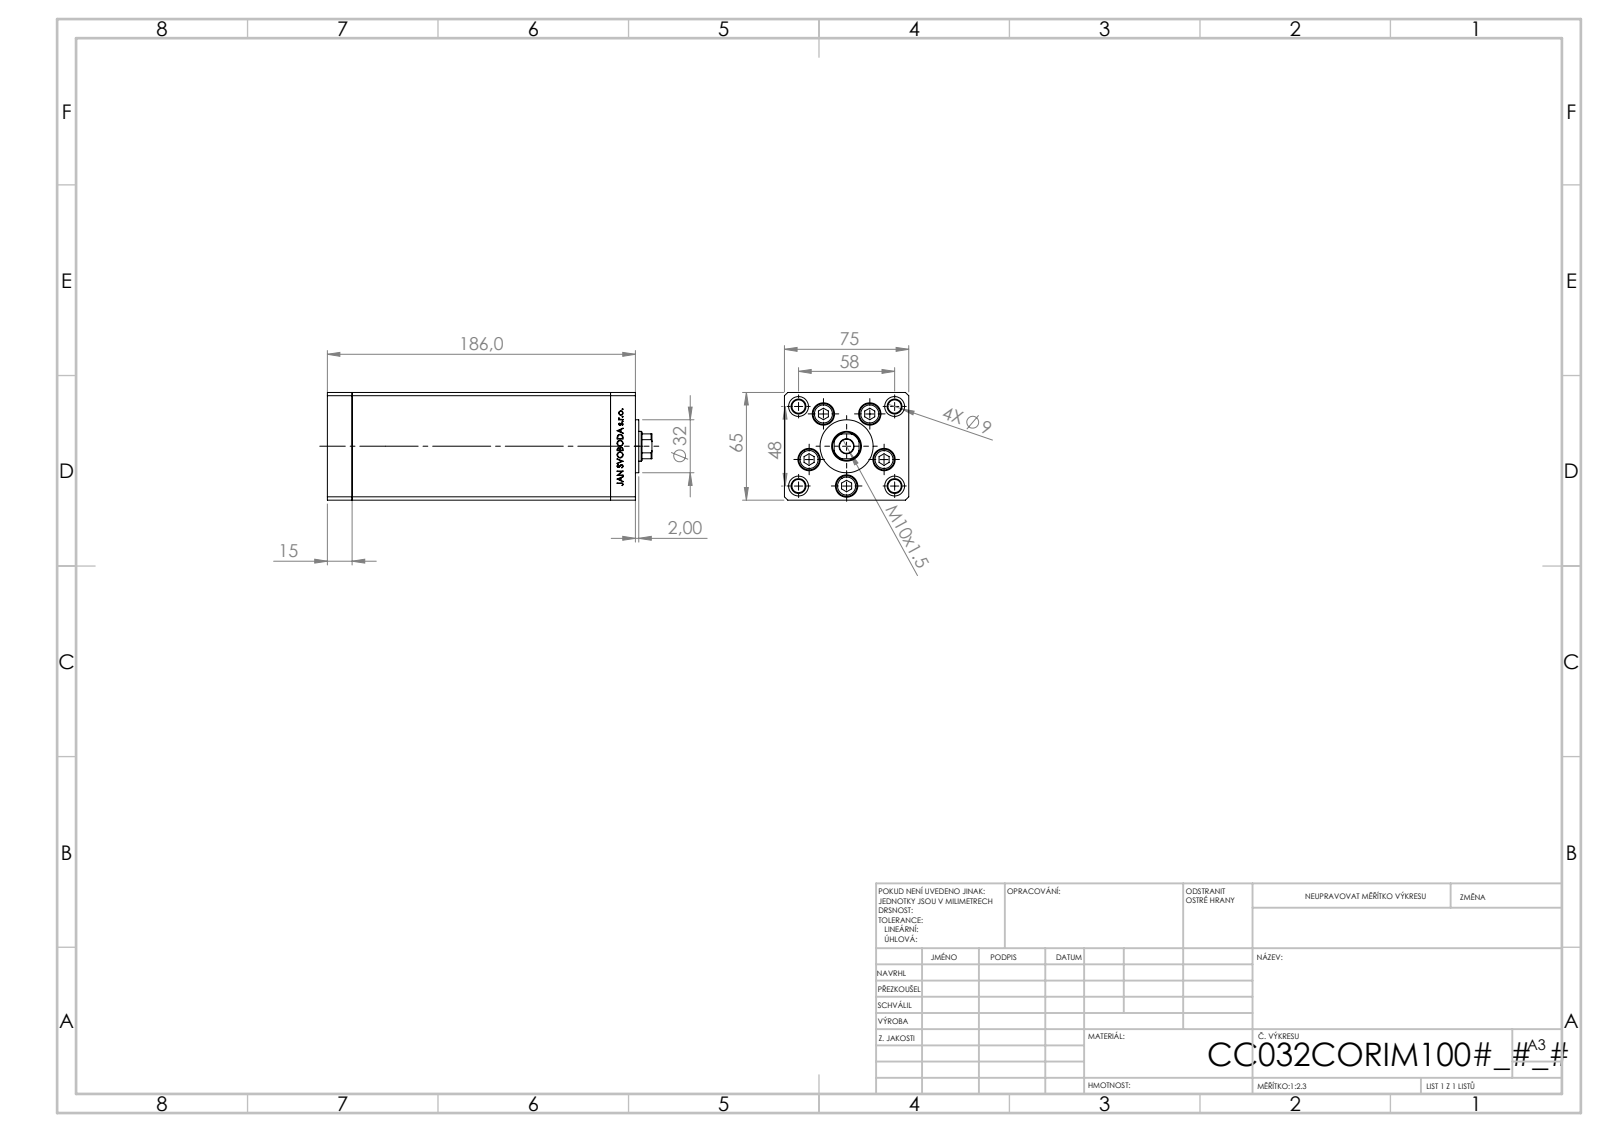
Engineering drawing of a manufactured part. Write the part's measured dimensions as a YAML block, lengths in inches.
part_name: "V220C FRONT; V220C_VC_C; ALLEN BOLT; V220C BACK_C (+1 more)"
step_written_by: "SolidWorks 2019 (CONFIG_CONTROL_DESIGN)"
units: inches
bodies: {solids: 13, faces: 1159, planar: 538, cylindrical: 159, other: 462}
overall_size: [7.717, 2.953, 2.559]
volume: 46.47
surface_area: 236.7
round_holes:
  - {diameter: 0.354, count: 9}
  - {diameter: 0.531, count: 5}
  - {diameter: 0.315, count: 4}
  - {diameter: 0.472, count: 4}
  - {diameter: 0.335, count: 1}
  - {diameter: 0.492, count: 1}
  - {diameter: 0.709, count: 1}
round_bosses_or_shafts:
  - {diameter: 0.315, count: 5}
  - {diameter: 0.492, count: 4}
  - {diameter: 1.26, count: 1}
partial_cylinders:
  - {radius: 0.037, count: 2}
  - {radius: 0.335, count: 1}
face_to_face_distances: [2.953, 2.559, 0.591, 6.142, 6.732, 7.323, 1.102, 2.146, 0.413, 1.033]
hole_center_spacings: [0.945, 1.482, 0.617, 0.678, 1.091, 1.135, 1.142, 1.285]
